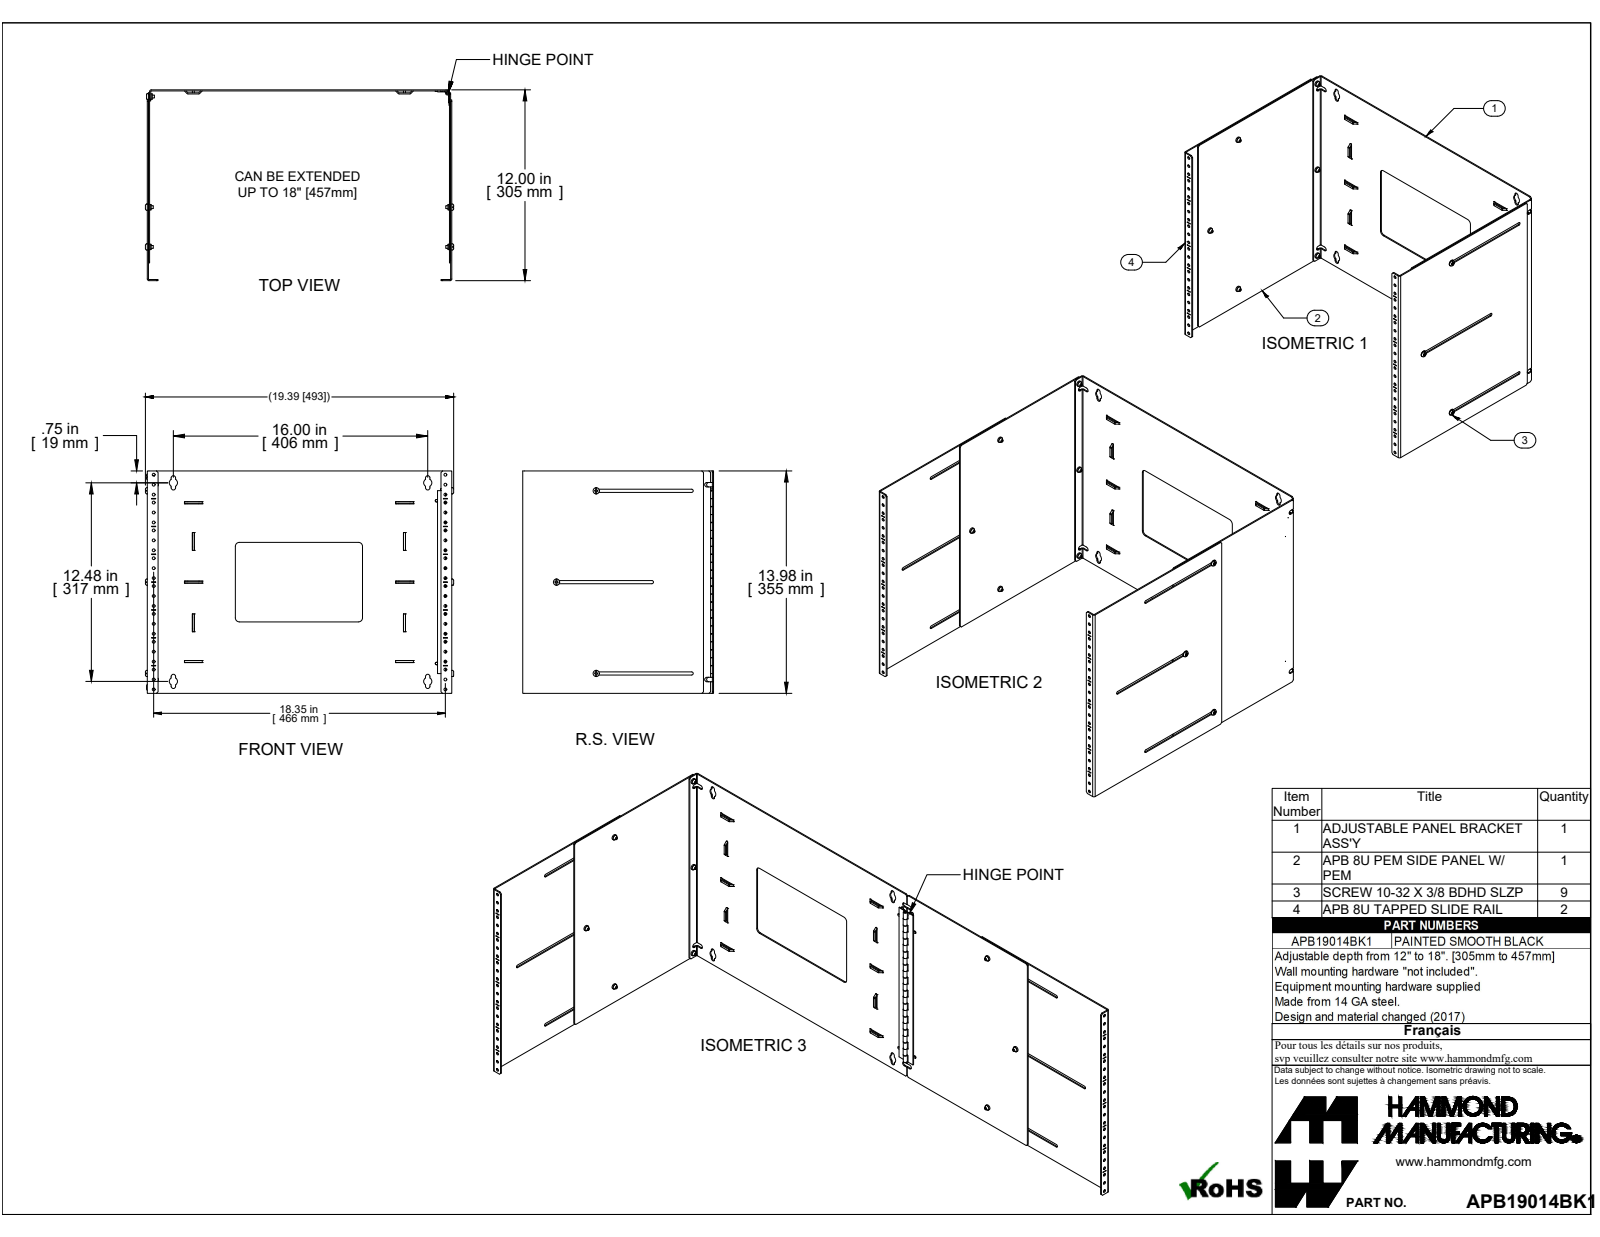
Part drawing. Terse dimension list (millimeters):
name: APB19014BK1
written by: SolidWorks 2019 (CONFIG_CONTROL_DESIGN)
unit: mm
bodies: 26 solids, 876 faces (584 planar, 244 cylindrical, 48 other)
size: 492.5 × 355.2 × 304.8
volume: 1 030 000 mm³; area: 1 156 000 mm²
holes: 48× ⌀4.5, 6× ⌀4, 6× ⌀6.4, 3× ⌀5.1, 1× ⌀3.4
bosses: 6× ⌀9.9, 6× ⌀8.6, 6× ⌀6.2, 6× ⌀4.6, 1× ⌀6.4, 1× ⌀3.2
rounds: 16× R1.8, 16× R3.6, 6× R2.5, 4× R6.4, 4× R6.6, 3× R0.9, 3× R2.7
face distances: 1.8, 482.9, 484.7, 481.1, 479.2, 3.7, 1.8, 481.1, 486.5, 482.9
hole spacings: 44.5, 88.9, 133.4, 177.8, 15.9, 15.9, 31.8, 222.3
